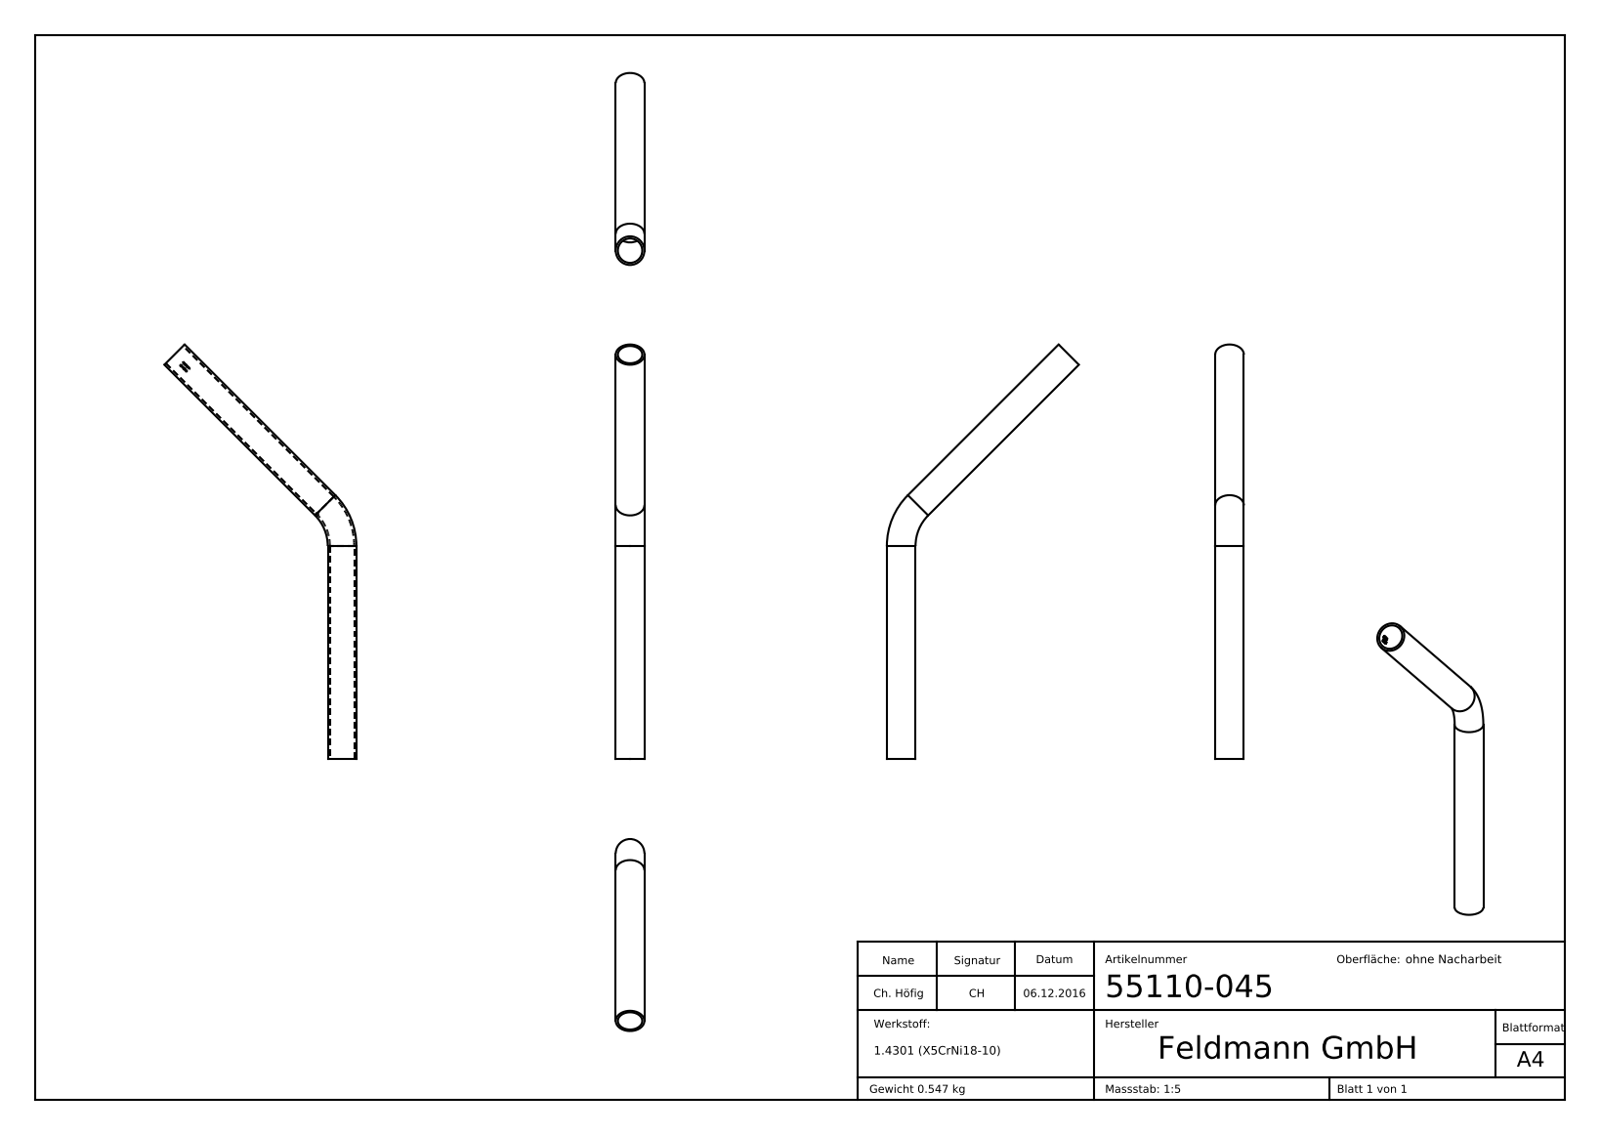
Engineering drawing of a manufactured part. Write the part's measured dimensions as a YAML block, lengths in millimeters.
part_name: "55110-045"
step_written_by: "SolidWorks 2015 (CONFIG_CONTROL_DESIGN)"
units: millimeters
bodies: {solids: 1, faces: 228, planar: 103, cylindrical: 31, other: 94}
overall_size: [389.12, 180.2, 26.9]
volume: 69215
surface_area: 69538
round_holes:
  - {diameter: 22.9, count: 2}
round_bosses_or_shafts:
  - {diameter: 26.9, count: 2}
partial_cylinders:
  - {radius: 11.55, count: 1}
face_to_face_distances: [1.02, 4.04, 1.41, 3.43, 2.41, 3.26, 3.87, 4.89, 0.85, 0.38]
